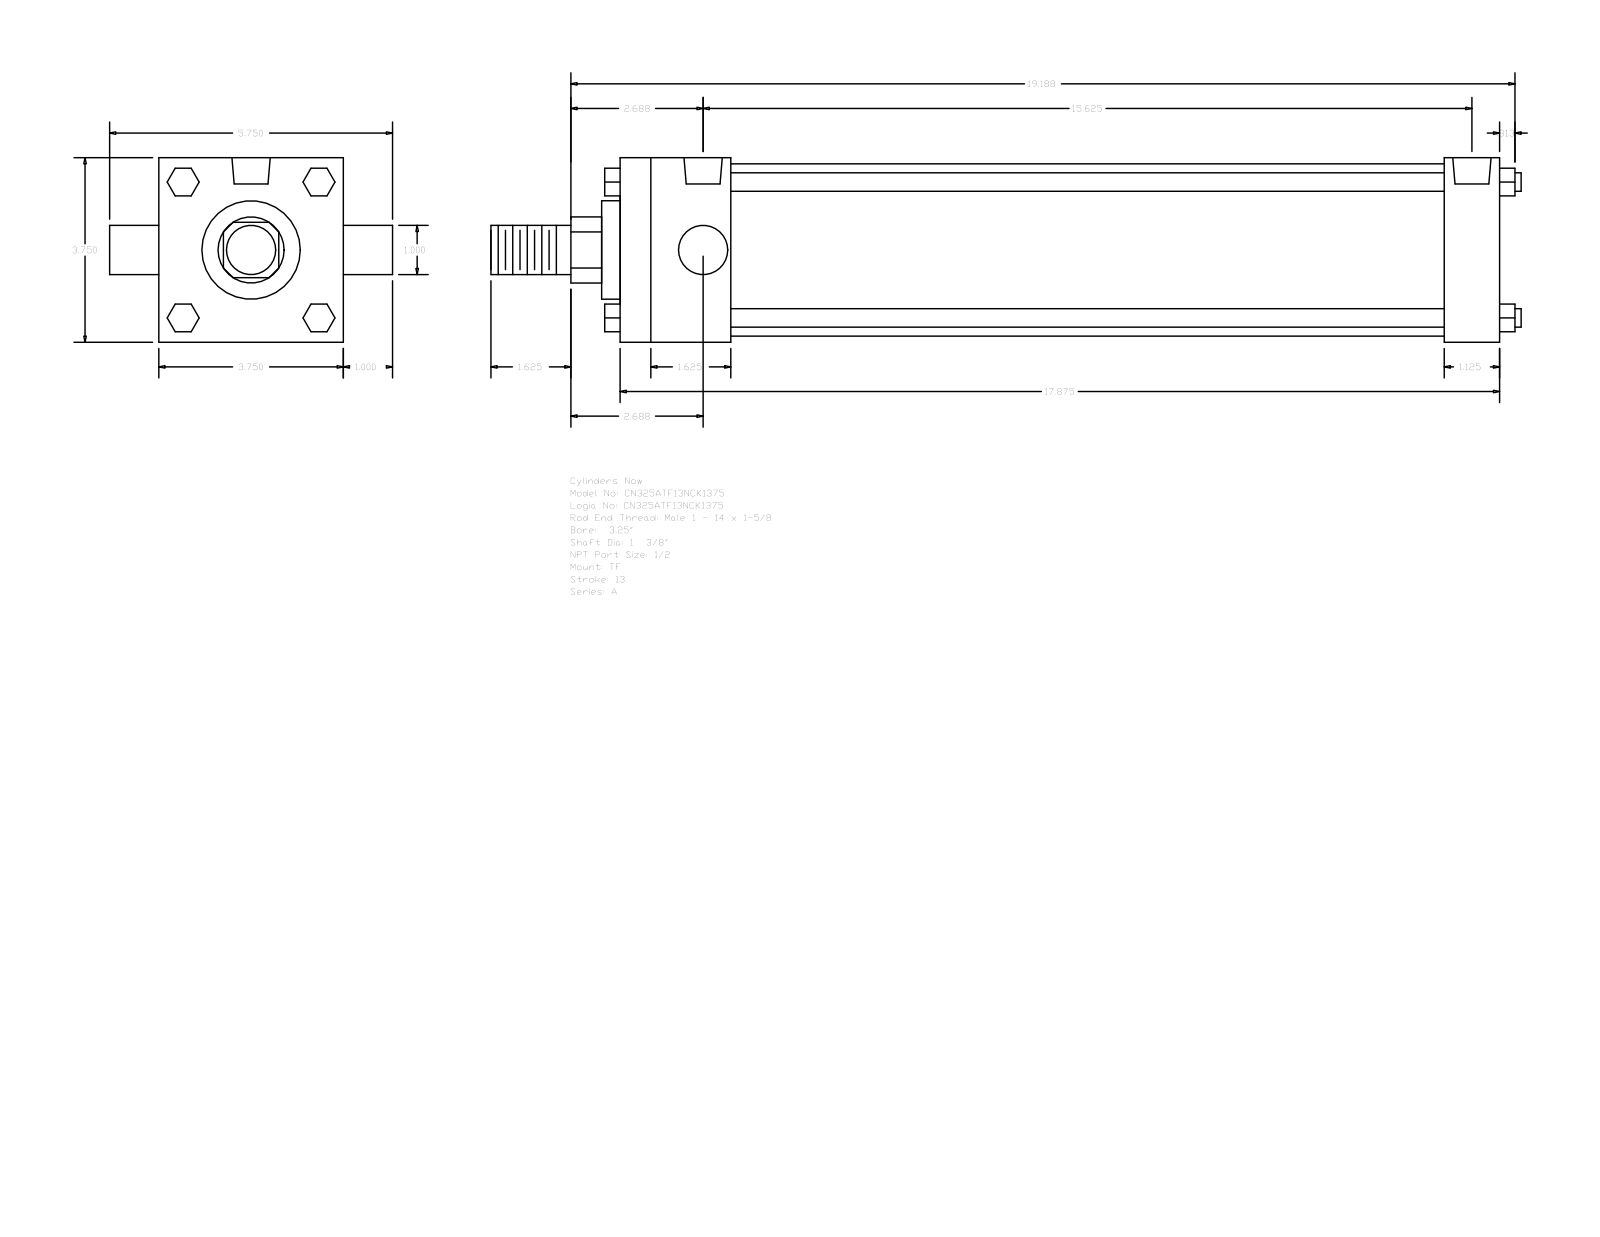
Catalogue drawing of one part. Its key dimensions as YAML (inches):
part_name: "A_TF__0325_1.375"
step_written_by: "GSSL Pune (CONFIG_CONTROL_DESIGN)"
units: inches
bodies: {solids: 0, faces: 120, planar: 92, cylindrical: 28, other: 0}
overall_size: [20.937, 5.75, 3.75]
round_holes:
  - {diameter: 0.344, count: 3}
  - {diameter: 0.778, count: 2}
round_bosses_or_shafts:
  - {diameter: 0.375, count: 4}
  - {diameter: 1, count: 2}
  - {diameter: 3.5, count: 1}
  - {diameter: 2, count: 1}
  - {diameter: 1.375, count: 1}
partial_cylinders:
  - {radius: 0.672, count: 1}
face_to_face_distances: [3.75, 17.875, 2.25, 1.125, 16.75, 14.5, 15.625, 2.625, 0.375, 17.125]
hole_center_spacings: [0.125, 15.5, 15.375, 15.625]
